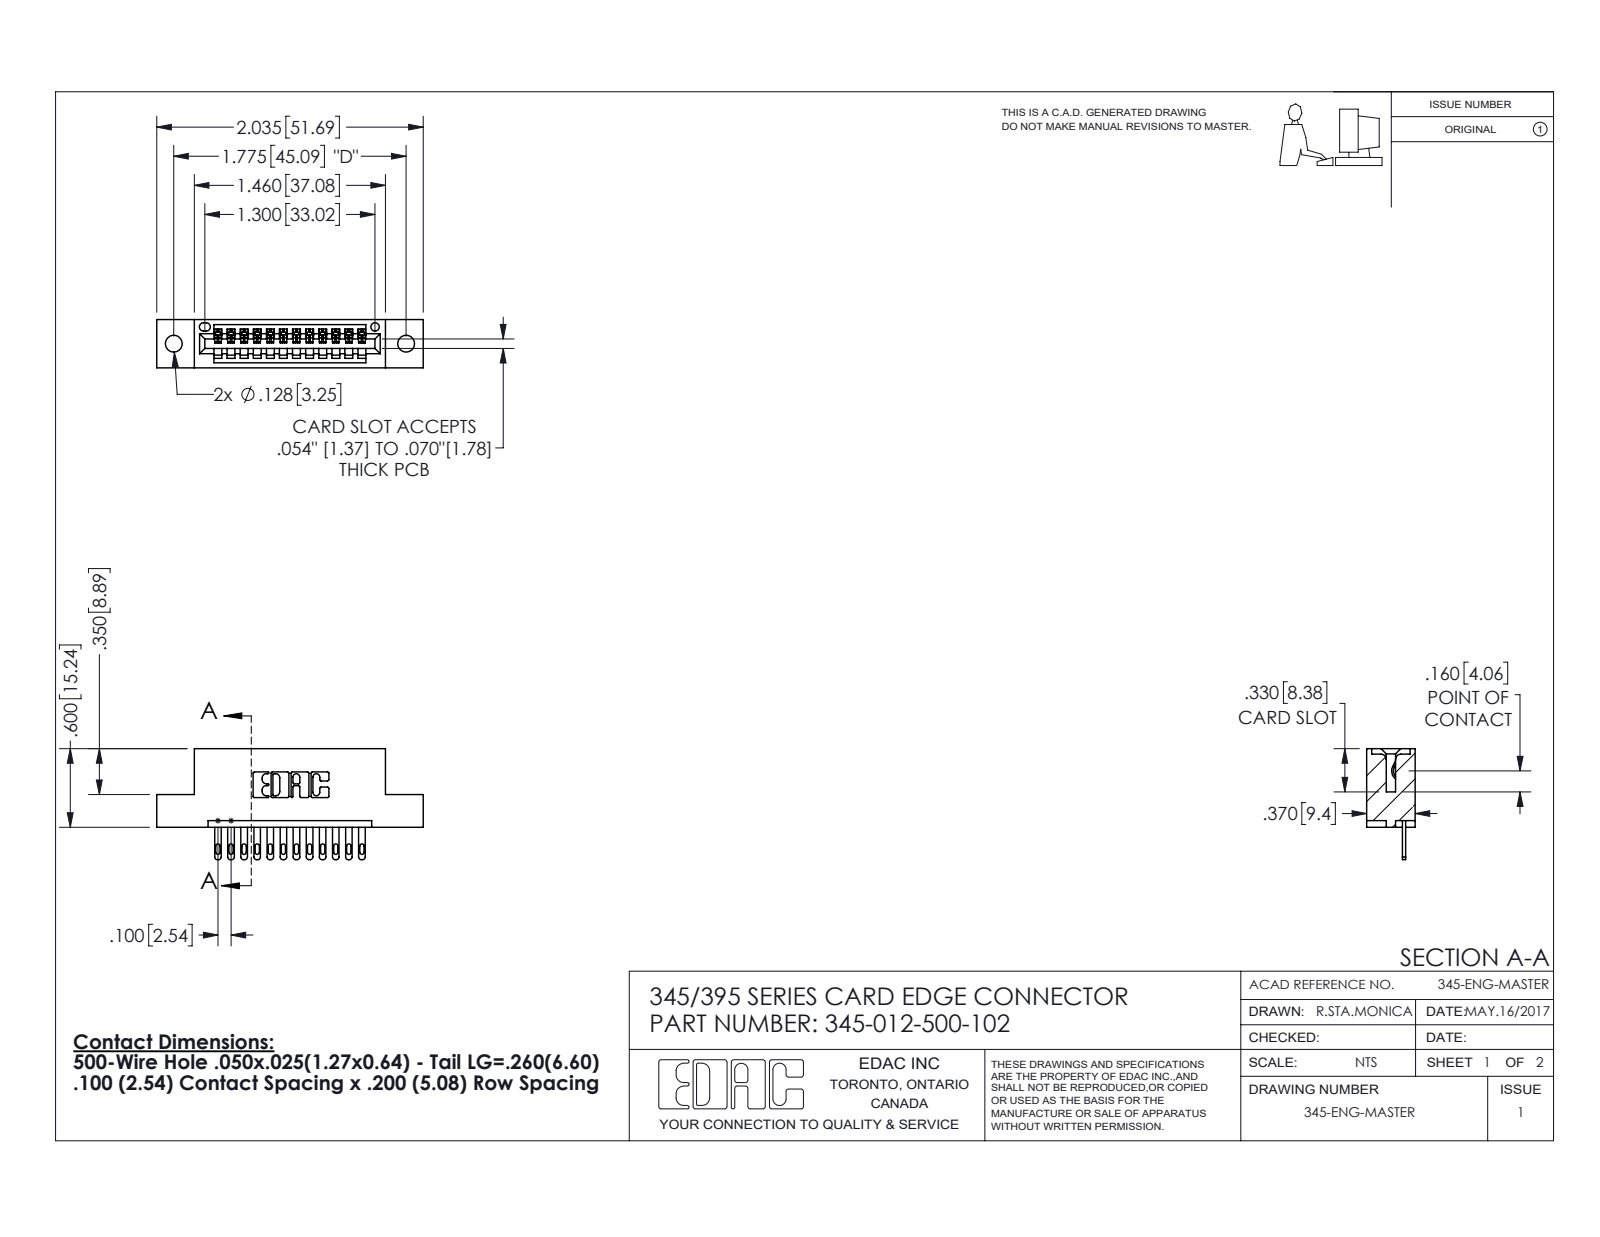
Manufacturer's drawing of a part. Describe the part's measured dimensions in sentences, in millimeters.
The part is named "345-012-500-102; 345-292-001_345-293-100; 345 Part_Flush Mounting Lugs - 0.128 Dia". Its 3-D file was written by "SolidWorks 2016 (CONFIG_CONTROL_DESIGN)". It is 13 solids with 774 faces: 488 planar, 286 cylindrical and 0 other. Overall it measures 51.7 by 21.5 by 9.4 millimeters. Its volume is 4 640 cubic millimeters and its surface area 5 506 square millimeters. Round holes: 2 of diameter 3.3, 1 of diameter 1.6. Partial cylindrical surfaces (rounded edges, fillets, slot ends): 24 of radius 0.2, 24 of radius 0.4, 24 of radius 0.5, 22 of radius 0.3, 6 of radius 0.2, 6 of radius 0.8, 3 of radius 0.7, 2 of radius 0.8. The main face-to-face distances are 5.1, 7.6, 1.8, 9.4, 2.5, 6.9, 0.6, 2.5, 15.2, 7.6. The hole center spacings are 6.9, 39.2, 45.1.
